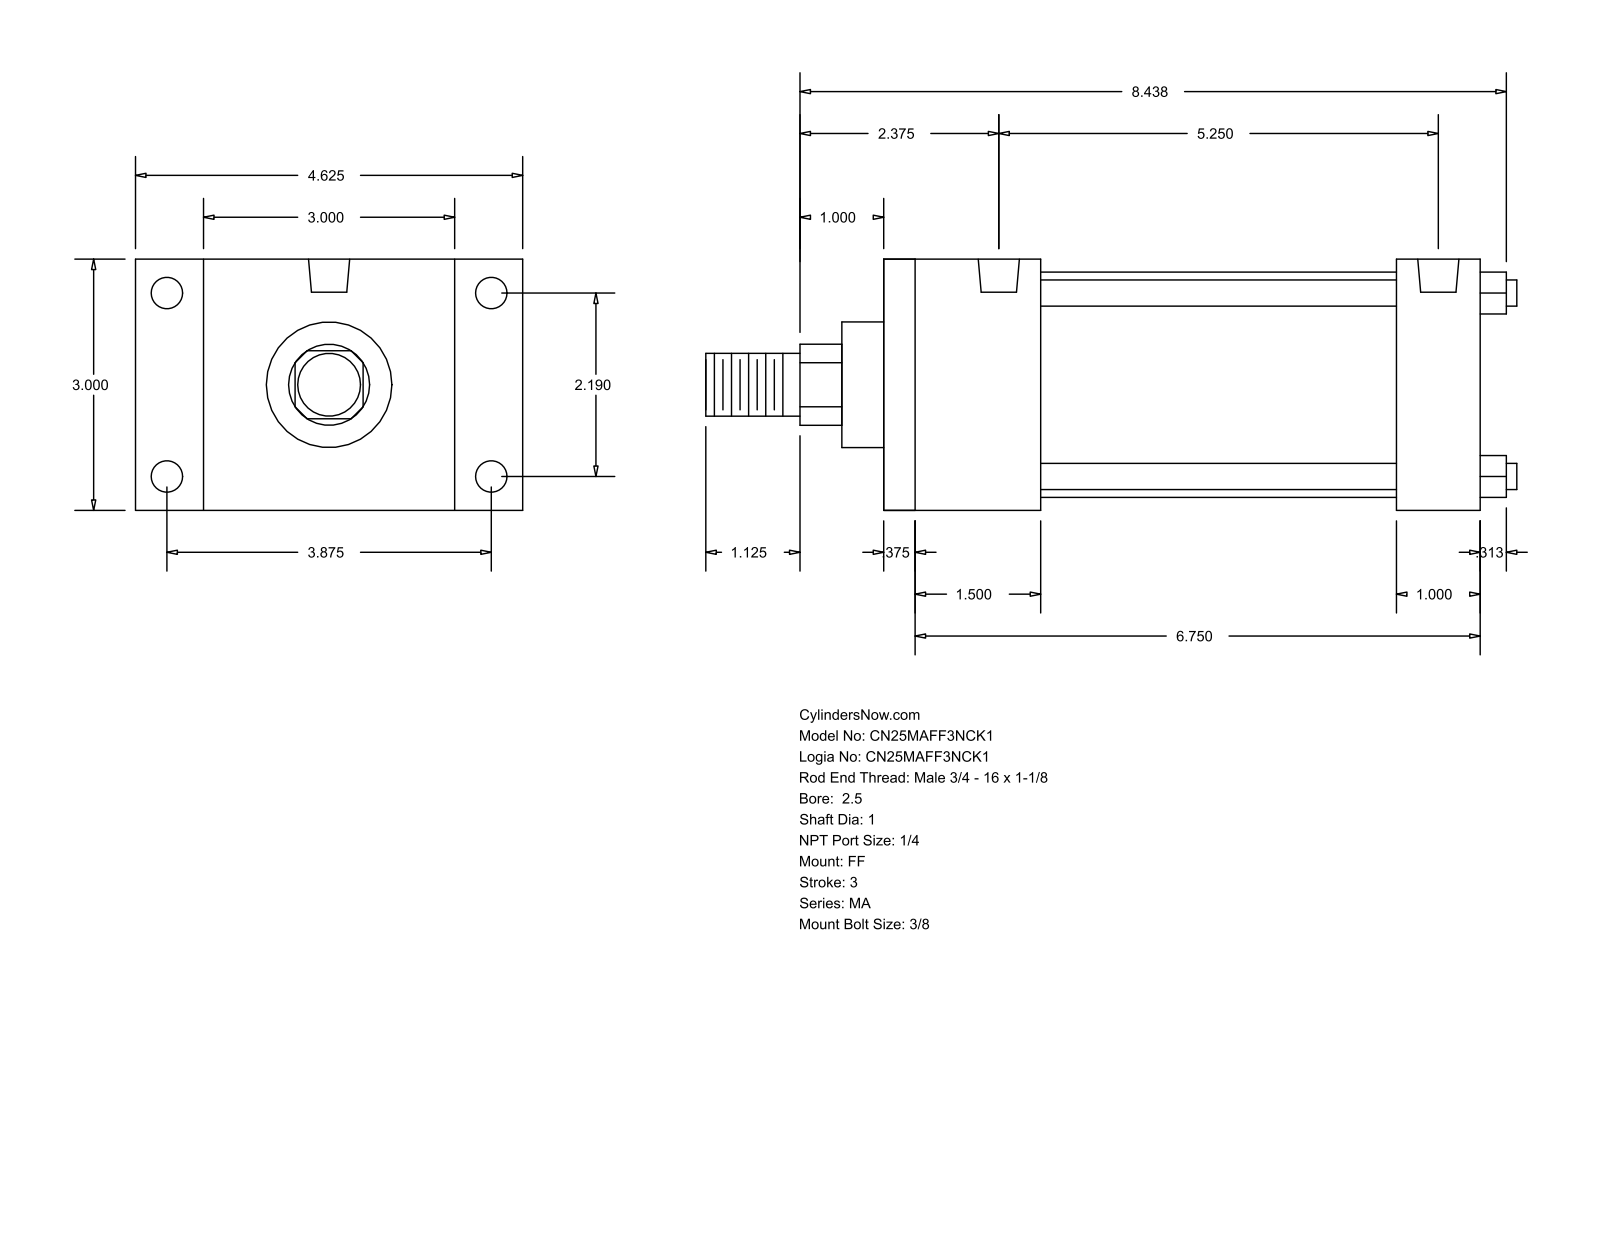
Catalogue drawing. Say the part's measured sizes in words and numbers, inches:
The part is named "MA_FF__0250_1". Its 3-D file was written by "GSSL Pune (CONFIG_CONTROL_DESIGN)". It is 0 solids with 92 faces: 64 planar, 28 cylindrical and 0 other. Overall it measures 9.687 by 4.625 by 3 inches. Round holes: 4 of diameter 0.313, 4 of diameter 0.375, 2 of diameter 0.492. Round bosses or shafts: 4 of diameter 0.313, 1 of diameter 2.69, 1 of diameter 1.5, 1 of diameter 1, 1 of diameter 0.75. Partial cylindrical surfaces (rounded edges, fillets, slot ends): 1 of radius 0.484. The main face-to-face distances are 3, 7.125, 0.375, 6.75, 1.875, 6.125, 1.5, 5.75, 4.25, 5.25. The hole center spacings are 2.19, 3.875, 4.451, 5.25.
